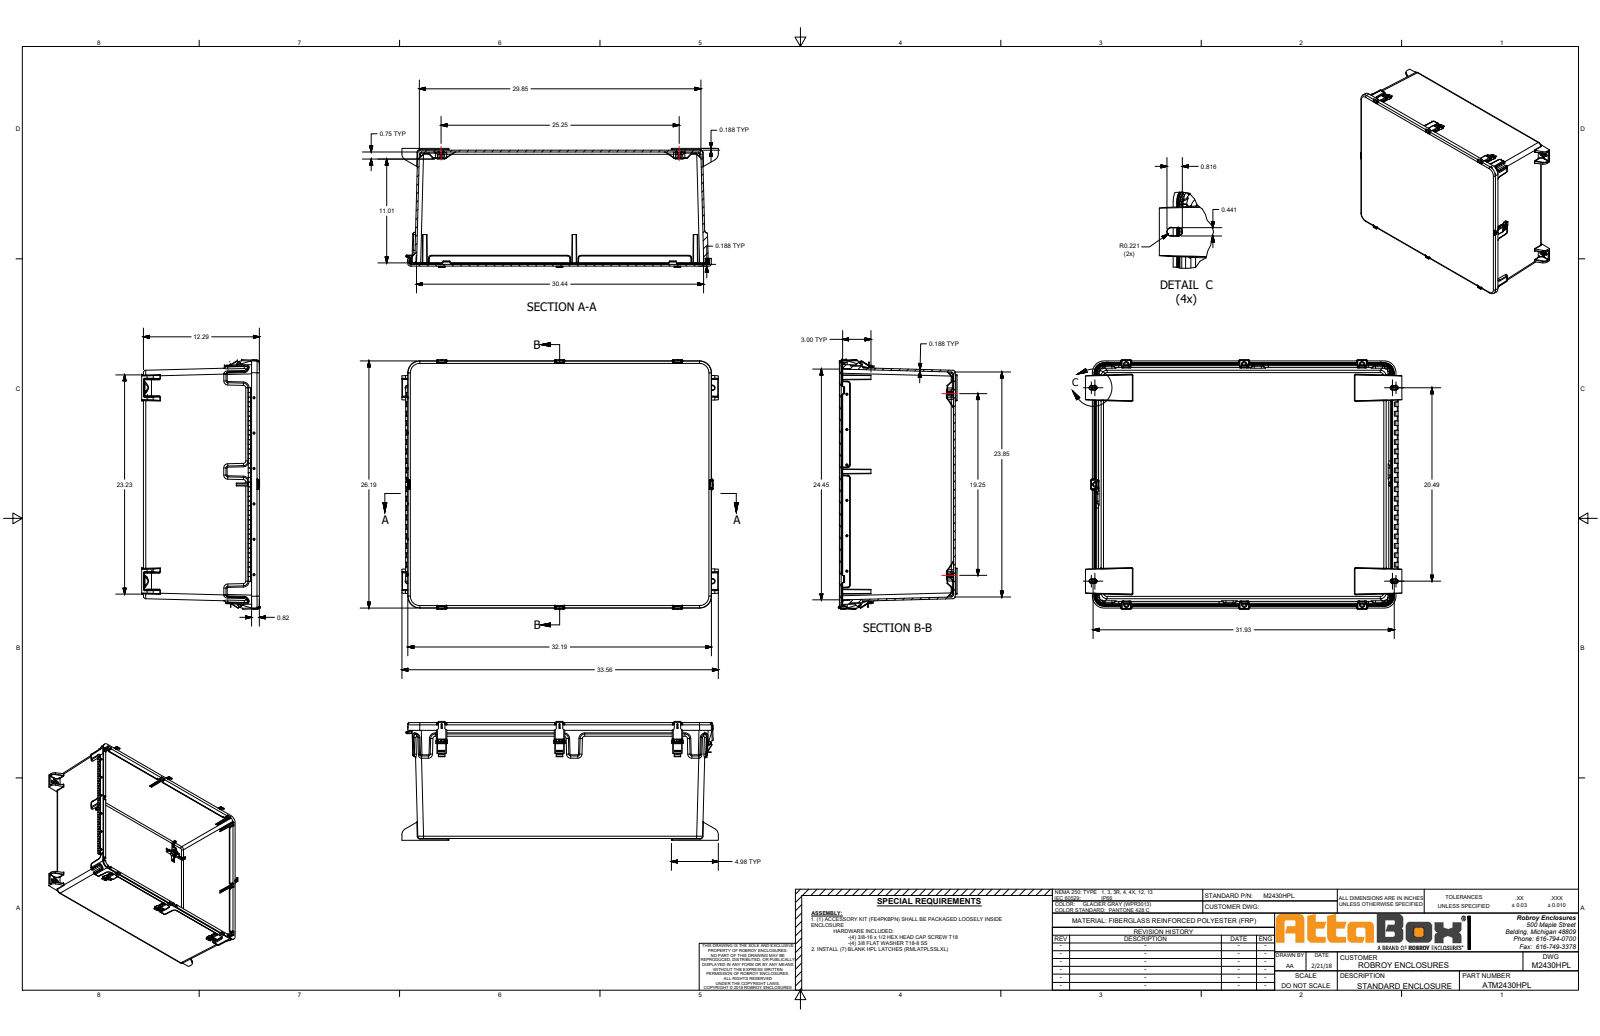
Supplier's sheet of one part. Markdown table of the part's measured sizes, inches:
| quantity | value |
| --- | --- |
| part name | M2430HPL |
| STEP written by | SolidWorks 2018 (AUTOMOTIVE_DESIGN) |
| units | inches |
| bodies | 50 solids, 4200 faces (1280 planar, 1544 cylindrical, 1376 other) |
| overall size | 33.556 × 26.461 × 12.598 |
| volume | 611.9 in³ |
| surface area | 6 389 in² |
| round holes (diameter × count) | 0.195 × 12, 0.196 × 12, 0.089 × 6, 0.135 × 6, 0.375 × 5, 0.075 × 4, 0.135 × 4, 0.309 × 4, 0.075 × 2, 0.375 × 2, 0.12 × 1, 0.125 × 1 |
| round bosses / shafts (diameter × count) | 0.125 × 8, 0.5 × 4, 0.125 × 4, 0.3 × 3, 0.24 × 1 |
| partial cylindrical surfaces (radius × count) | 0.05 × 116, 0.02 × 104, 0.063 × 100, 0.005 × 84, 0.125 × 58, 0.25 × 58, 0.015 × 56, 0.03 × 56 |
| main face-to-face distances | 0.188, 12.098, 0.188, 12.286, 11.909, 0.439, 0.294, 0.482, 0.154, 0.145 |
| hole center spacings | 3.75, 7.5, 0.439, 11.25, 3.384, 4.13, 7.13, 7.877 |
